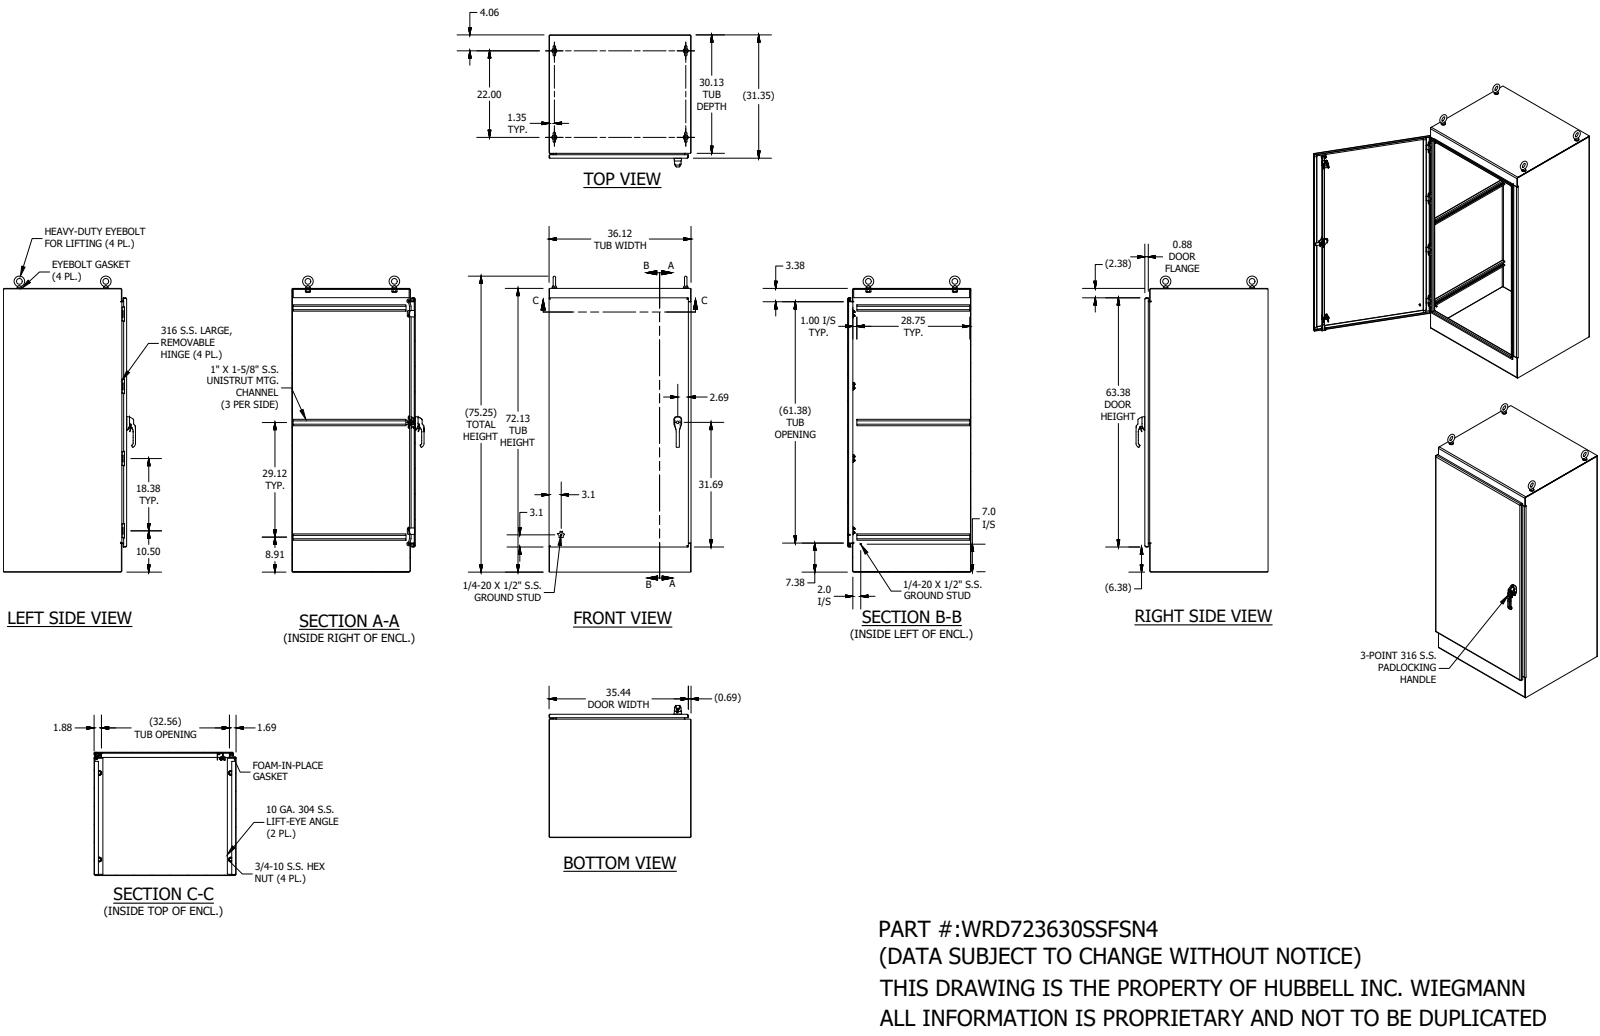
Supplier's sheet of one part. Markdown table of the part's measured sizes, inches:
| quantity | value |
| --- | --- |
| part name | WRD723630SSFSN4 |
| STEP written by | SolidWorks 2019 (AUTOMOTIVE_DESIGN) |
| units | inches |
| bodies | 109 solids, 4029 faces (1604 planar, 1394 cylindrical, 1031 other) |
| overall size | 75.248 × 36.129 × 33.598 |
| volume | 1 473 in³ |
| surface area | 27 527 in² |
| round holes (diameter × count) | 0.14 × 24, 0.195 × 8, 0.262 × 8, 0.266 × 8, 0.294 × 8, 0.65 × 8, 0.136 × 4, 0.164 × 4, 0.187 × 4, 0.201 × 4, 0.642 × 4, 0.813 × 4 |
| round bosses / shafts (diameter × count) | 0.625 × 8, 0.25 × 7, 1.25 × 4, 1.12 × 4, 0.75 × 4, 0.237 × 4, 0.236 × 3, 1 × 2 |
| partial cylindrical surfaces (radius × count) | 0.02 × 172, 0.012 × 114, 0.125 × 34, 0.019 × 21, 0.062 × 18, 0.05 × 14, 0.063 × 14, 0.079 × 14 |
| main face-to-face distances | 0.104, 36.021, 31.245, 31.141, 35.917, 0.104, 31.349, 31.245, 72.021, 36.125 |
| hole center spacings | 0.018, 0.017, 0.023, 0.38, 0.76, 1, 18.375, 36.75 |
